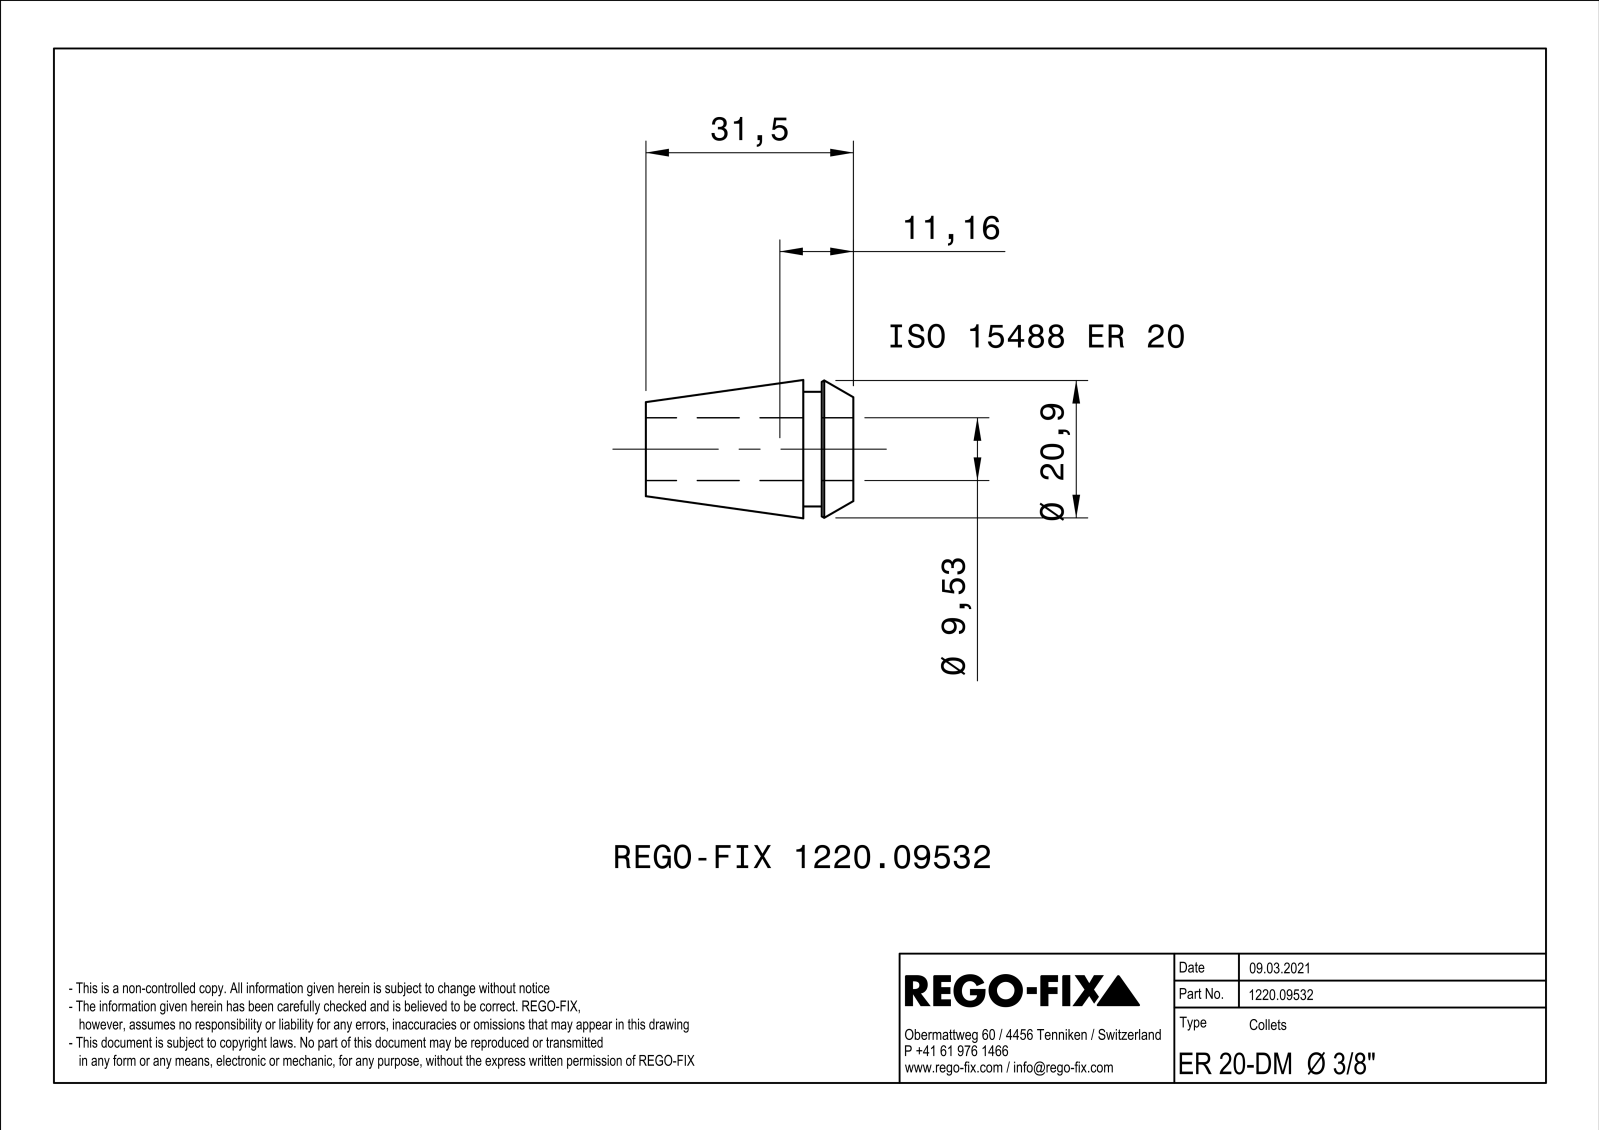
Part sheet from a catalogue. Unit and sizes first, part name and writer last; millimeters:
Units: millimetres
Overall size (bounding box): 31.5 × 20.98 × 20.98
Round holes (diameter × count): ⌀9.53 ×1
Round bosses / shafts (diameter × count): ⌀17.4 ×1
Main face-to-face distances: 0.8, 7.6, 4.8, 2.8, 31.5, 26.7, 23.9, 14, 9.2, 6.4
Volume: 4 485 mm³ · Surface area: 5 443 mm²
Bodies: 1 solid, 154 faces (80 planar, 9 cylindrical, 65 other)
Part name (STEP PRODUCT): NOCUT
STEP written by: SIEMENS PLM Software Solid Edge ST10 (AUTOMOTIVE_DESIGN)
